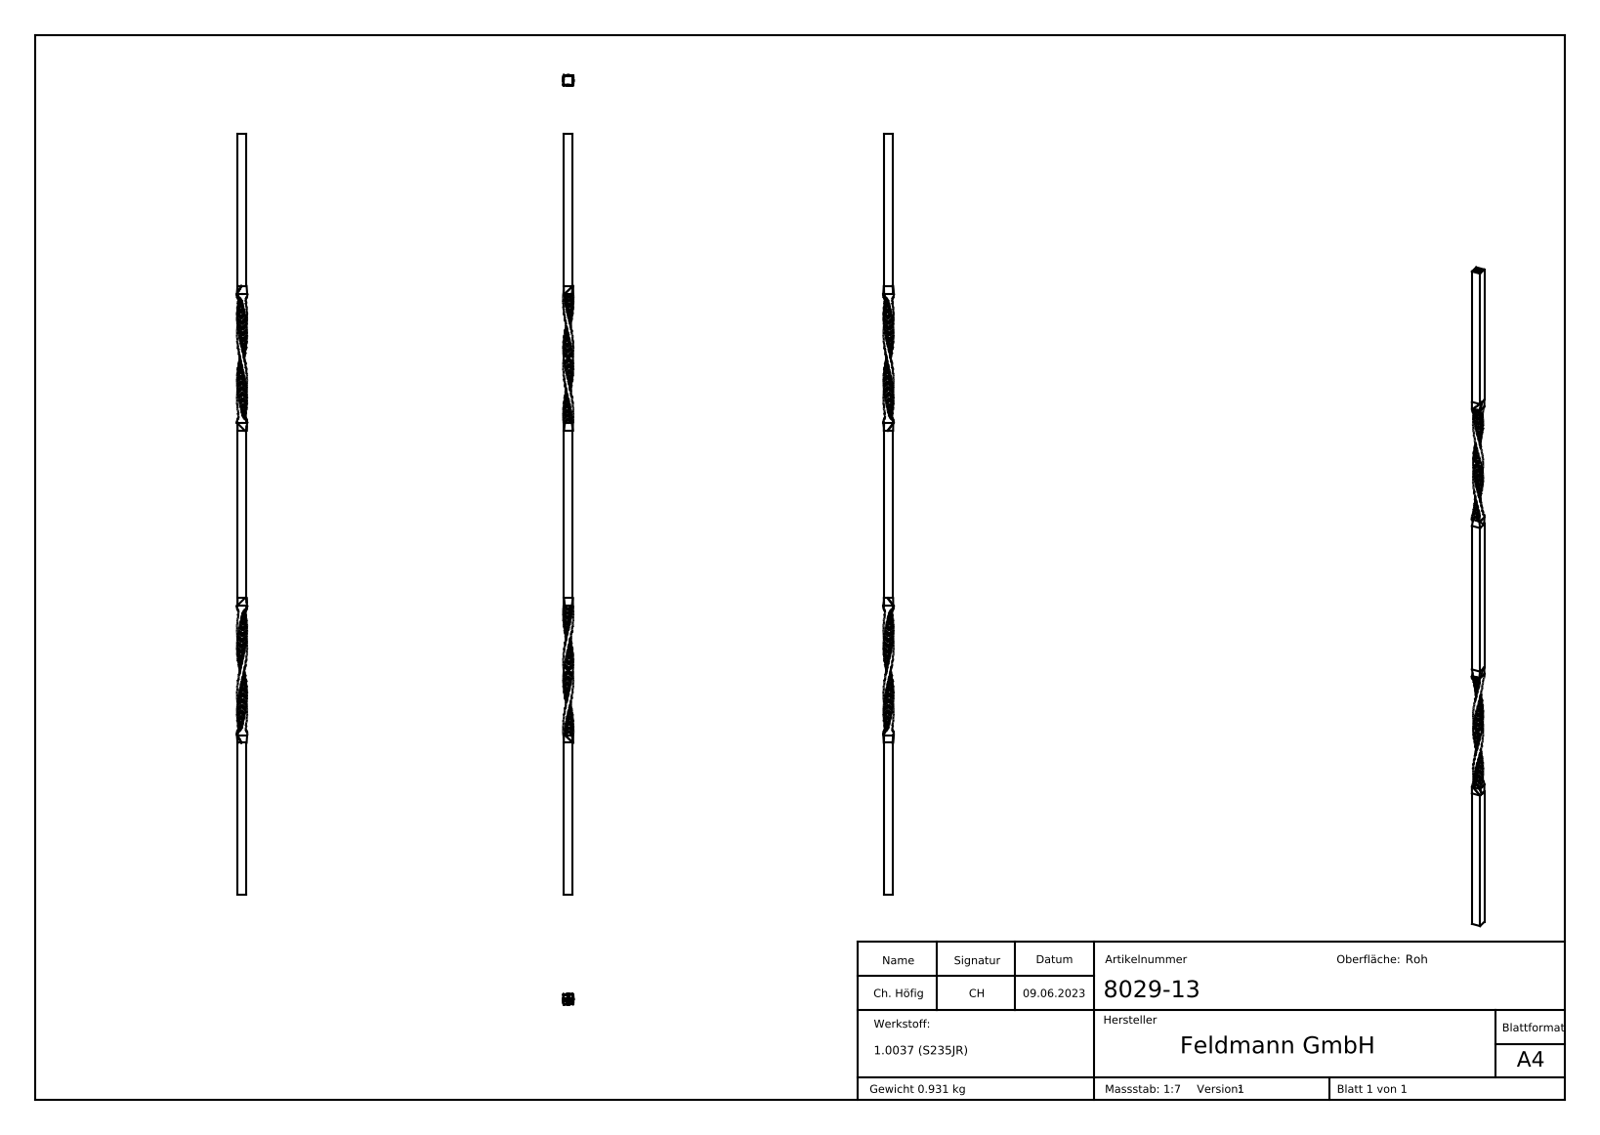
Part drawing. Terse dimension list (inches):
name: 8029-13
written by: SolidWorks 2018 (CONFIG_CONTROL_DESIGN)
unit: in
bodies: 1 solid, 1174 faces (173 planar, 0 cylindrical, 1001 other)
size: 39.37 × 0.716 × 0.558
volume: 7.282 in³; area: 69.87 in²
face distances: 0.472, 39.37, 39.366, 8.268, 31.102, 14.961, 24.409, 6.693, 16.142, 8.264
